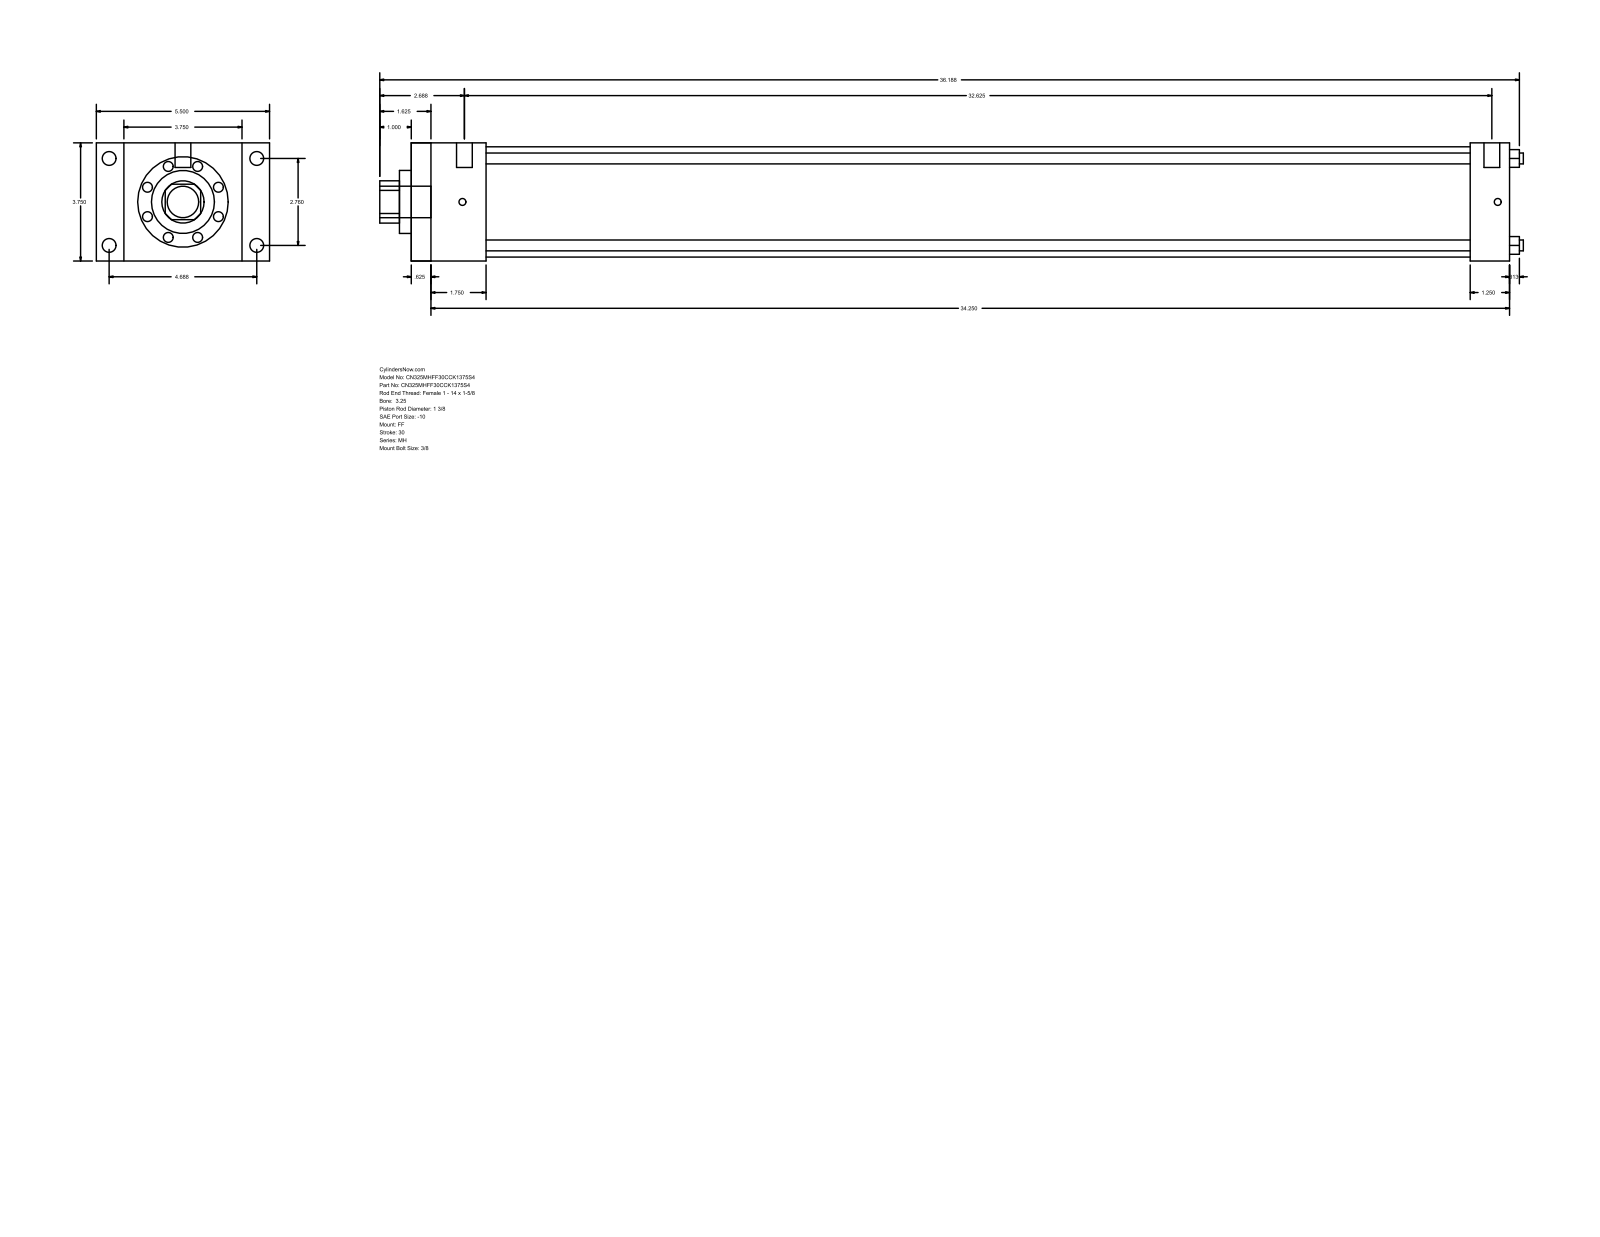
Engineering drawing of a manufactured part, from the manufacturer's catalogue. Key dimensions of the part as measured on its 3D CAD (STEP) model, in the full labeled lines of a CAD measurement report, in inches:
Part name (STEP PRODUCT): MH_FF__0325_1.375
STEP written by: GSSL Pune (CONFIG_CONTROL_DESIGN)
Units: inches
Bodies: 0 solids, 92 faces (64 planar, 28 cylindrical, 0 other)
Overall size (bounding box): 36.313 × 5.5 × 3.75
Round holes (diameter × count): ⌀0.345 ×4, ⌀1.375 ×1, ⌀2 ×1, ⌀3.5 ×1
Round bosses / shafts (diameter × count): ⌀0.438 ×4, ⌀0.219 ×4, ⌀0.5 ×2, ⌀1 ×1
Partial cylindrical surfaces — rounded edges, fillets, slot ends (radius × count): R0.672 ×1
Main face-to-face distances: 3.75, 34.875, 0.625, 34.25, 0.875, 4.625, 33.625, 33, 1.25, 2.375
Hole centre spacings: 1.952, 2.76, 3.903
